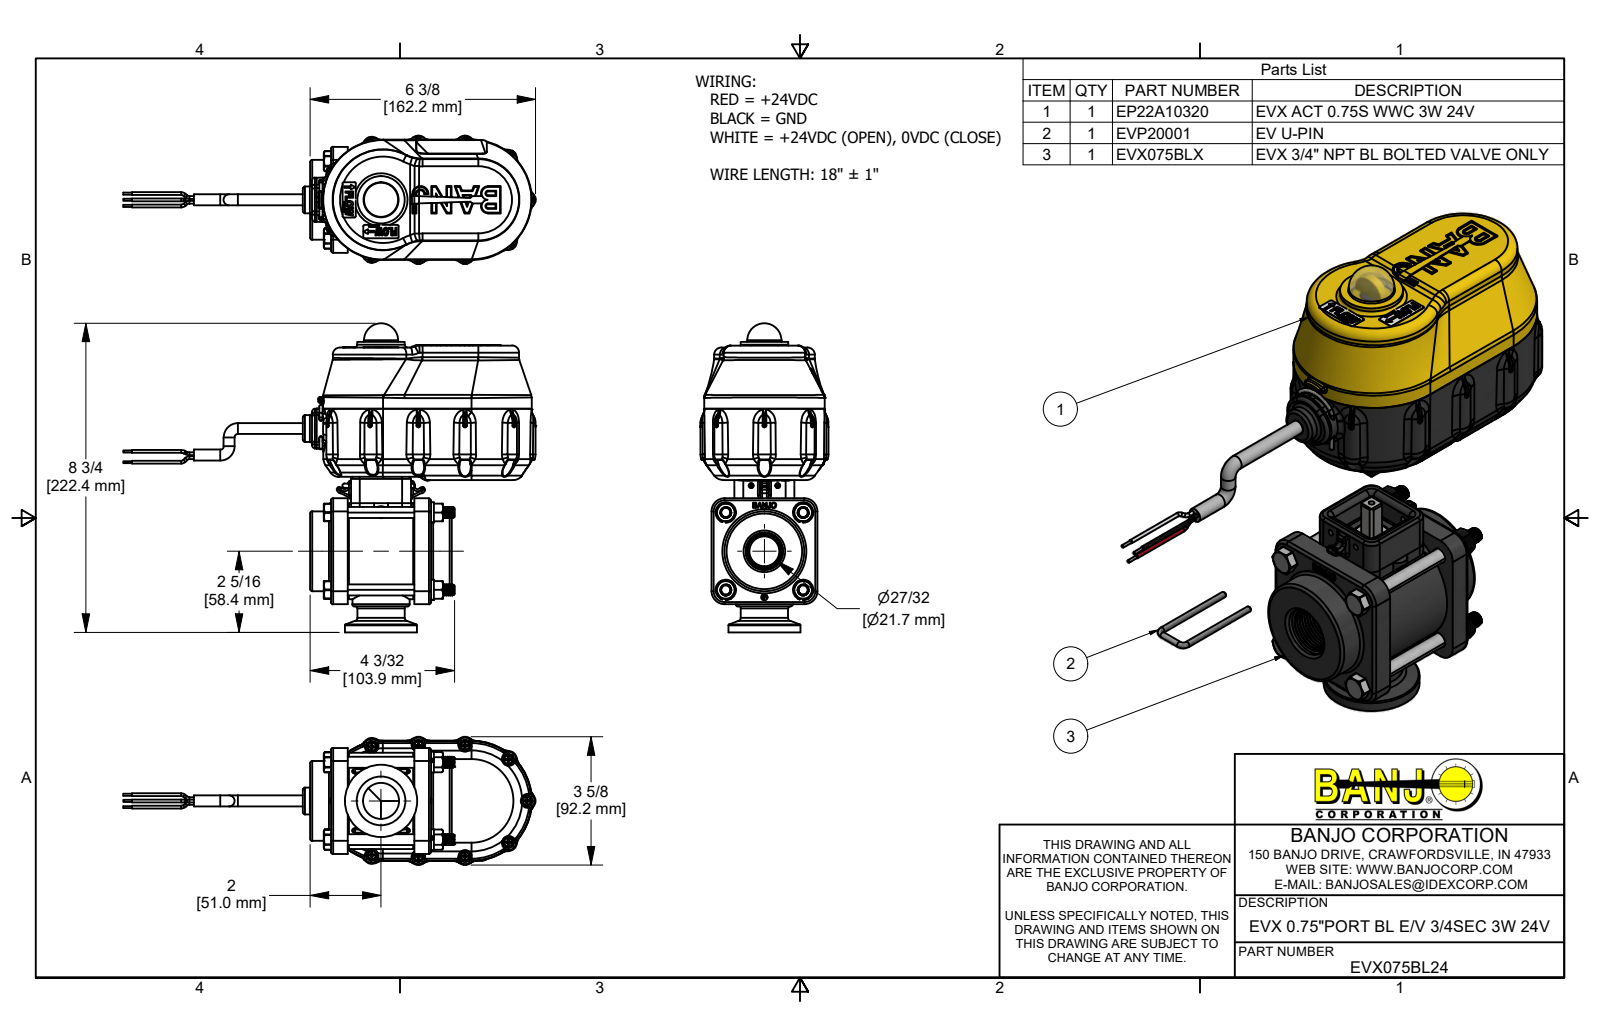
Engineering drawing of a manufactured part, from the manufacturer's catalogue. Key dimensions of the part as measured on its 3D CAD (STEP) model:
Part name (STEP PRODUCT): EVX075BL24; EVX075BLX; MEVX10354AB; MEVX10354ABX (+8 more)
STEP written by: Autodesk Inventor 2019 (AUTOMOTIVE_DESIGN)
Units: inches
Bodies: 98 solids, 12131 faces (3289 planar, 3483 cylindrical, 5359 other)
Overall size (bounding box): 30.214 × 8.757 × 3.63
Volume: 53.99 in³ · Surface area: 910.8 in²
Round holes (diameter × count): ⌀0.095 ×11, ⌀0.15 ×11, ⌀0.08 ×7, ⌀0.107 ×4, ⌀0.126 ×4, ⌀0.135 ×4, ⌀0.136 ×4, ⌀0.148 ×4, ⌀0.15 ×4, ⌀0.17 ×4, ⌀0.252 ×4, ⌀0.322 ×4
Round bosses / shafts (diameter × count): ⌀0.268 ×60, ⌀0.25 ×17, ⌀0.08 ×15, ⌀0.14 ×11, ⌀0.108 ×11, ⌀0.085 ×11, ⌀0.058 ×6, ⌀0.313 ×5
Partial cylindrical surfaces — rounded edges, fillets, slot ends (radius × count): R0.013 ×180, R0.04 ×145, R0.01 ×84, R0.02 ×72, R0.06 ×58, R0.005 ×53, R0.03 ×38, R0.08 ×28
Main face-to-face distances: 0.1, 2.565, 0.055, 0.211, 0.06, 0.151, 0.475, 2.36, 2.95, 0.125
Hole centre spacings: 1.046, 1.55, 1.662, 1.891, 2.192, 2.656, 2.69, 2.715
